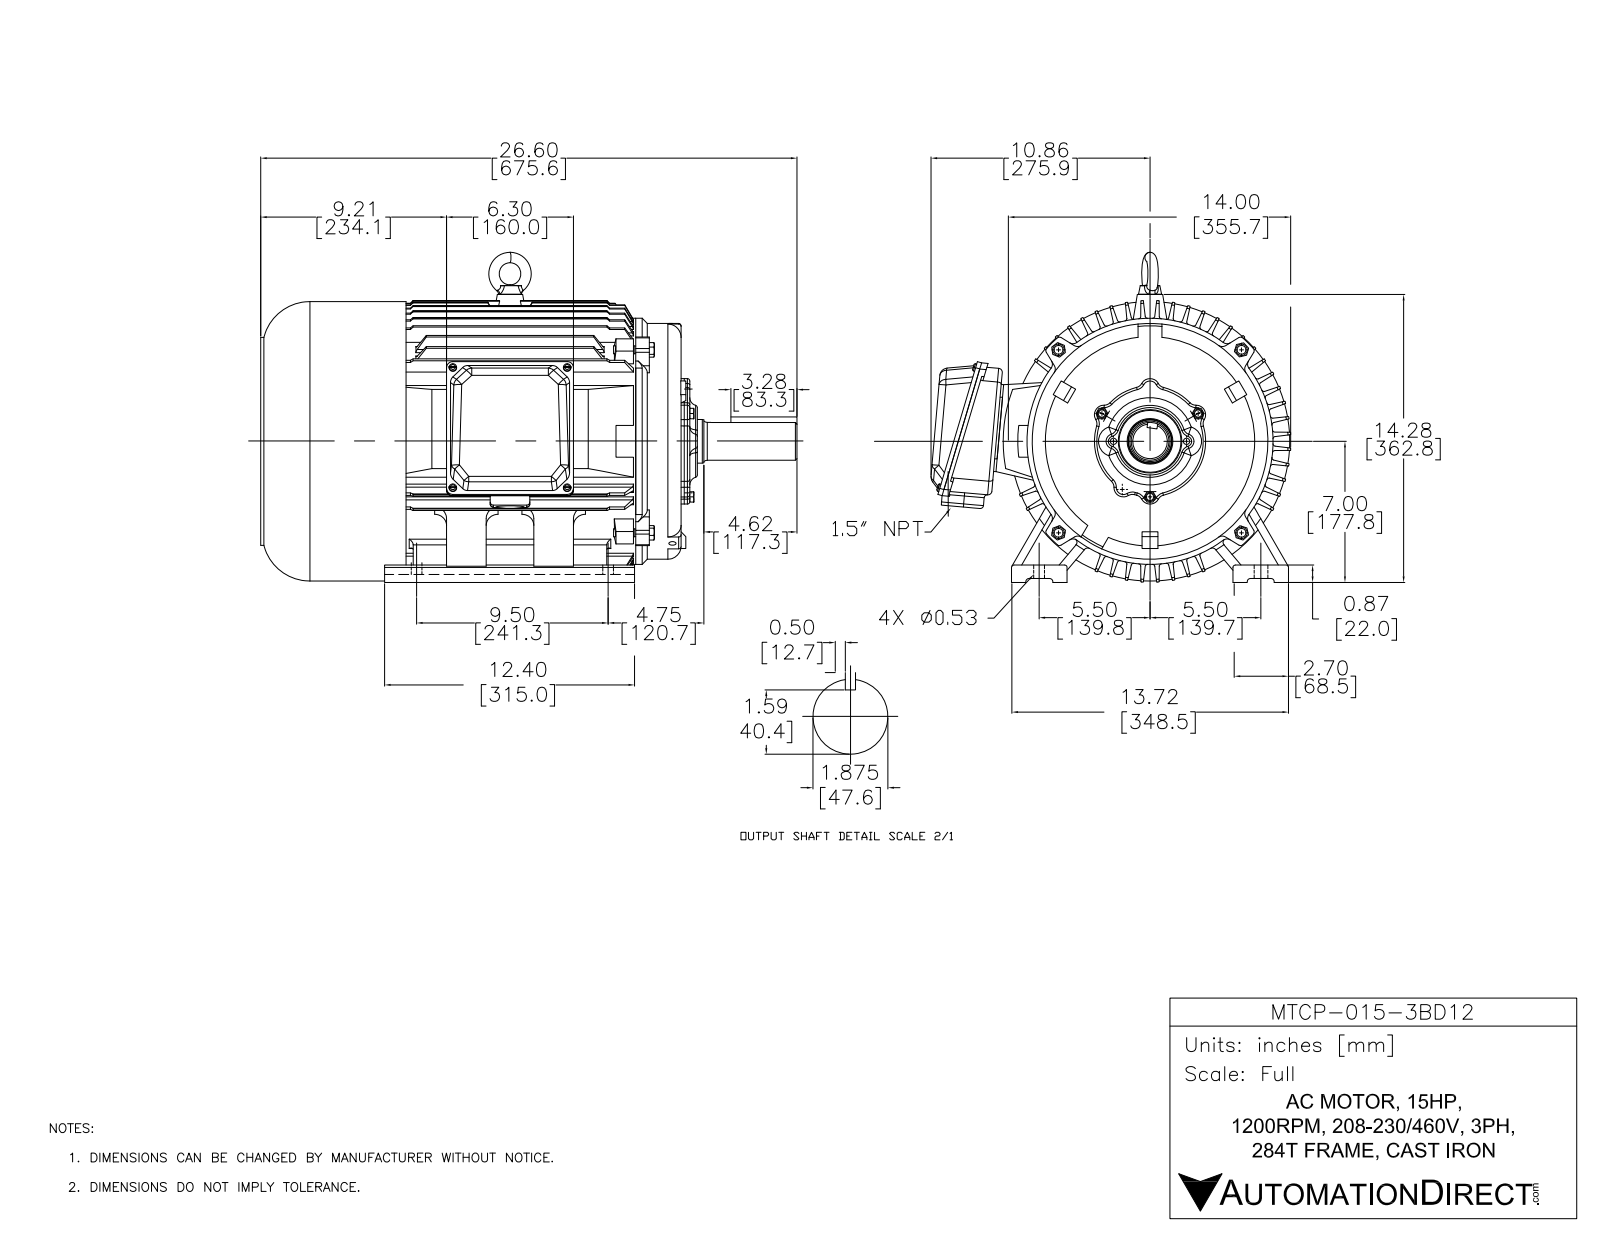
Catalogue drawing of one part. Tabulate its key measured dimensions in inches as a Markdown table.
| quantity | value |
| --- | --- |
| part name | PEWWE-284T-4,6,8 |
| STEP written by | SolidWorks 2017 (AUTOMOTIVE_DESIGN) |
| units | inches |
| bodies | 18 solids, 4173 faces (2137 planar, 1818 cylindrical, 218 other) |
| overall size | 26.6 × 17.843 × 16.374 |
| volume | 1 542 in³ |
| surface area | 3 250 in² |
| round holes (diameter × count) | 0.276 × 8, 0.394 × 7, 0.197 × 4, 0.441 × 4, 0.472 × 4, 0.551 × 4, 0.362 × 3, 0.315 × 2, 0.354 × 2, 0.335 × 1, 0.402 × 1, 0.669 × 1 |
| round bosses / shafts (diameter × count) | 0.355 × 4, 0.197 × 4, 0.315 × 3, 0.283 × 3, 13.858 × 1, 12.205 × 1, 11.693 × 1, 10.315 × 1 |
| partial cylindrical surfaces (radius × count) | 0.02 × 1308, 0.118 × 72, 0.157 × 42, 0.394 × 26, 0.315 × 24, 0.197 × 13, 0.472 × 5, 0.63 × 4 |
| main face-to-face distances | 0.197, 0.315, 13.644, 0.866, 0.472, 20.848, 7.205, 0.236, 13.329, 20.533 |
| hole center spacings | 5.669, 6.22, 8.416, 2.756, 2.953, 5.294, 6.417, 7.804 |
